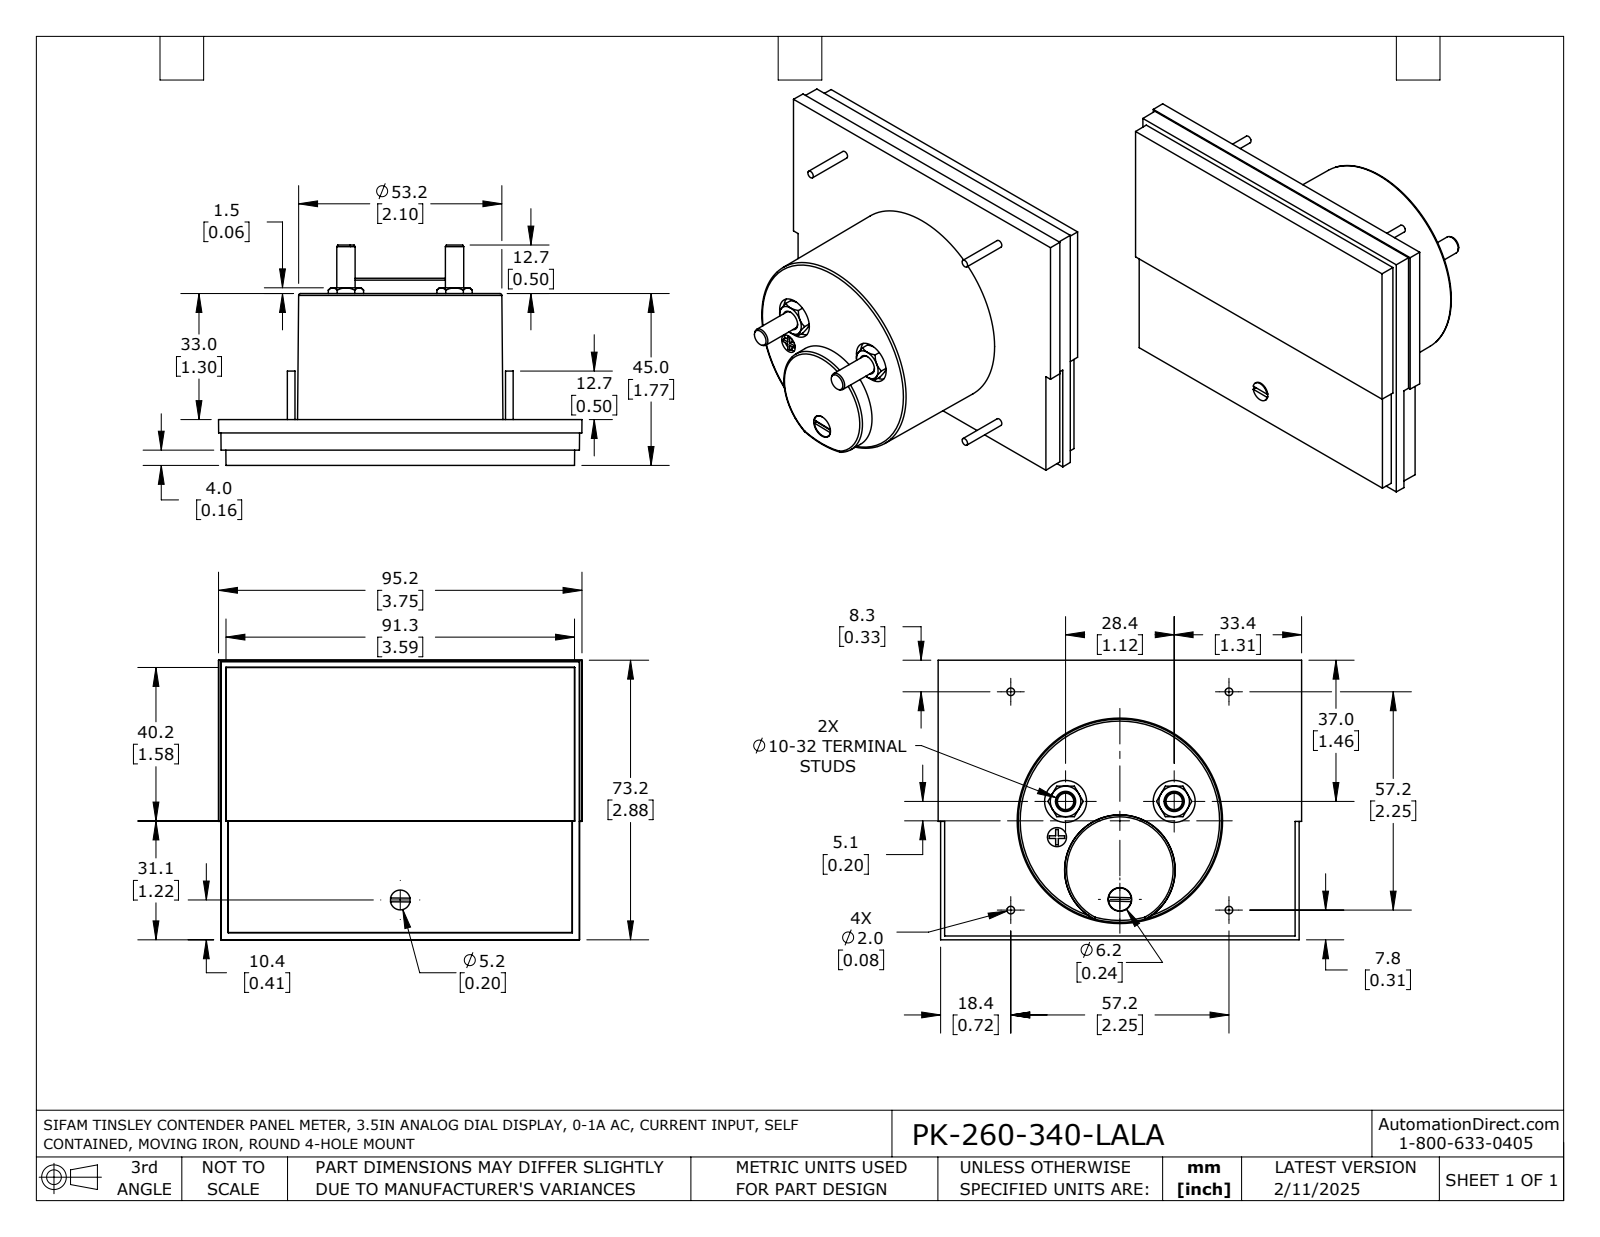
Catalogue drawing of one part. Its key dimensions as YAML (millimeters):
part_name: "PK-260-340-LALA"
step_written_by: "SolidWorks 2021 (AUTOMOTIVE_DESIGN)"
units: millimeters
bodies: {solids: 1, faces: 163, planar: 76, cylindrical: 31, other: 56}
overall_size: [95.2, 73.2, 57.7]
volume: 154800
surface_area: 24770
round_holes:
  - {diameter: 11, count: 2}
  - {diameter: 5, count: 1}
  - {diameter: 6.2, count: 1}
round_bosses_or_shafts:
  - {diameter: 2, count: 4}
  - {diameter: 4.8, count: 2}
  - {diameter: 6, count: 1}
  - {diameter: 5.2, count: 1}
partial_cylinders:
  - {radius: 2.5, count: 1}
face_to_face_distances: [12, 0.8, 11.3, 45, 33, 44.2, 4, 1.9, 8, 37]
hole_center_spacings: [29.3, 9.6, 23.2, 28.4, 32.1]
